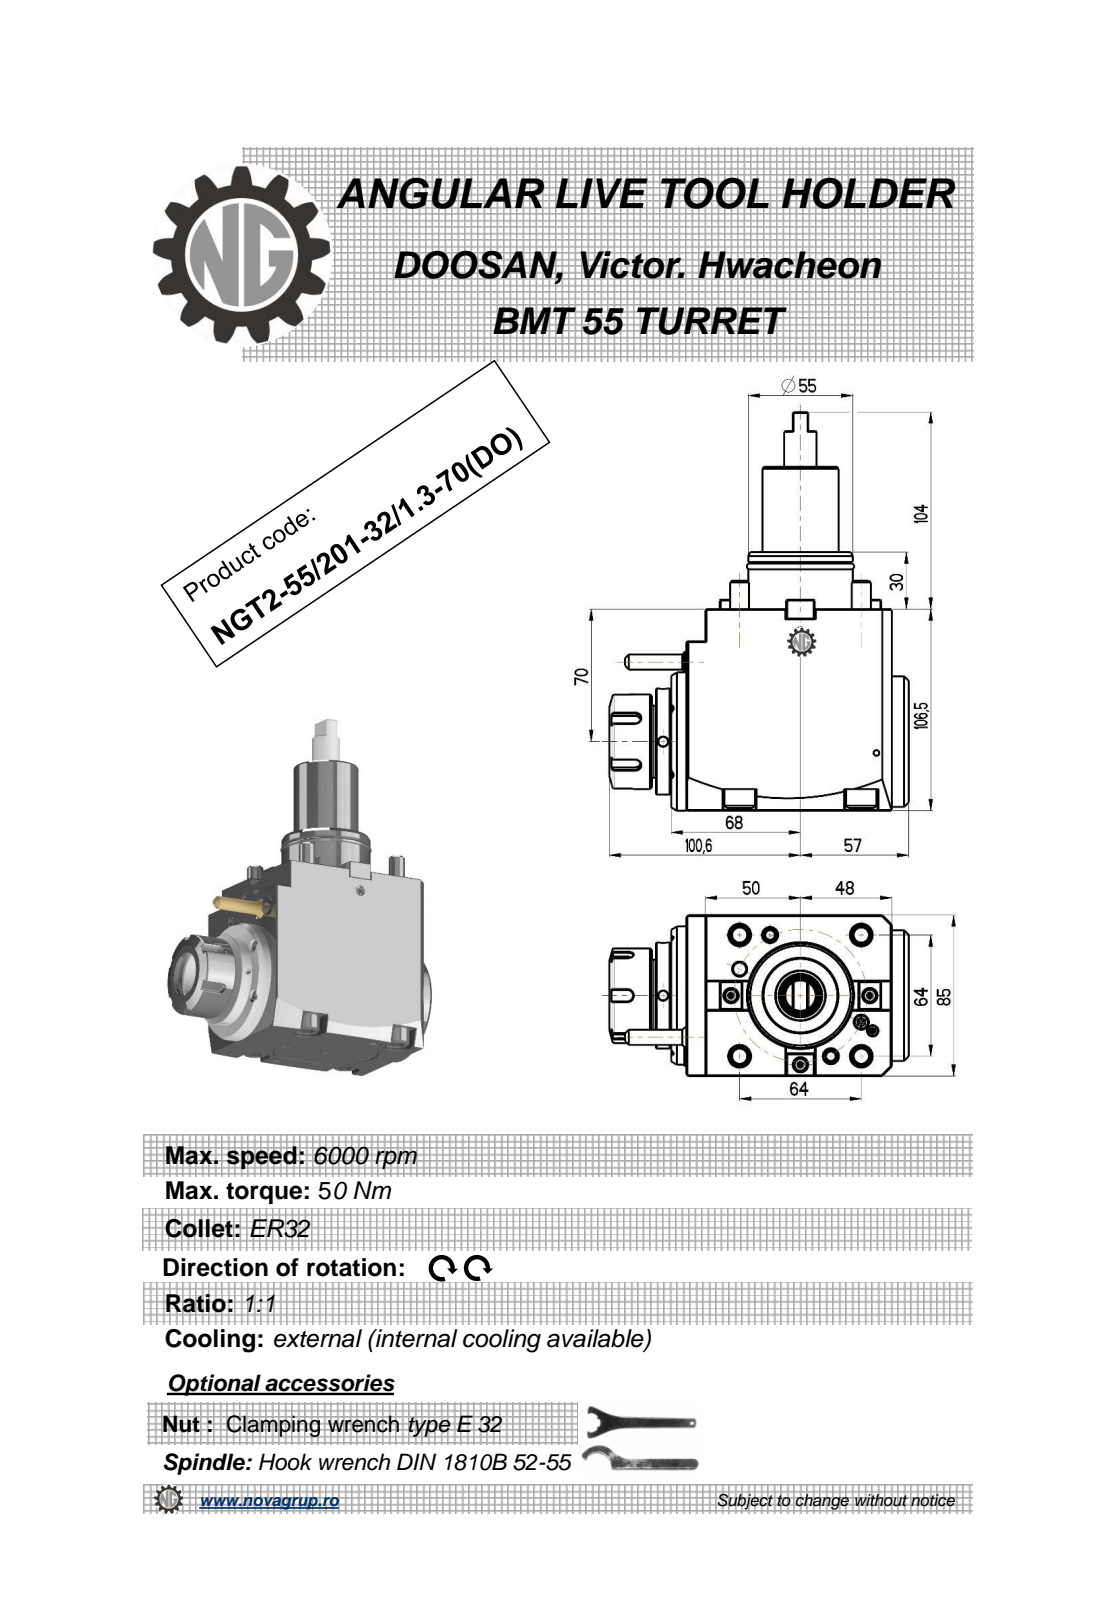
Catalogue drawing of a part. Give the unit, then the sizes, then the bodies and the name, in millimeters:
Units: millimetres
Overall size (bounding box): 210.5 × 157.6 × 85
Round holes (diameter × count): ⌀5 ×3, ⌀6.8 ×2, ⌀3 ×1, ⌀12 ×1, ⌀27 ×1
Round bosses / shafts (diameter × count): ⌀16 ×4, ⌀10 ×4, ⌀50 ×2, ⌀73 ×1, ⌀69 ×1, ⌀56 ×1, ⌀55 ×1, ⌀43.4 ×1
Partial cylindrical surfaces — rounded edges, fillets, slot ends (radius × count): R0.32 ×20, R0.22 ×6, R3 ×5, R8.5 ×4, R0.8 ×2, R480 ×2
Main face-to-face distances: 85, 106.5, 9, 8, 125, 108, 117, 116, 10, 18
Hole centre spacings: 42.62, 47.41, 69.86, 105.19
Volume: 1 207 000 mm³ · Surface area: 106 364 mm²
Bodies: 2 solids, 472 faces (228 planar, 111 cylindrical, 133 other)
Part name (STEP PRODUCT): NGT2_55_201_32_1_3_70_DO
STEP written by: PRO/ENGINEER BY PARAMETRIC TECHNOLOGY CORPORATION, 2010280 (CONFIG_CONTROL_DESIGN)
